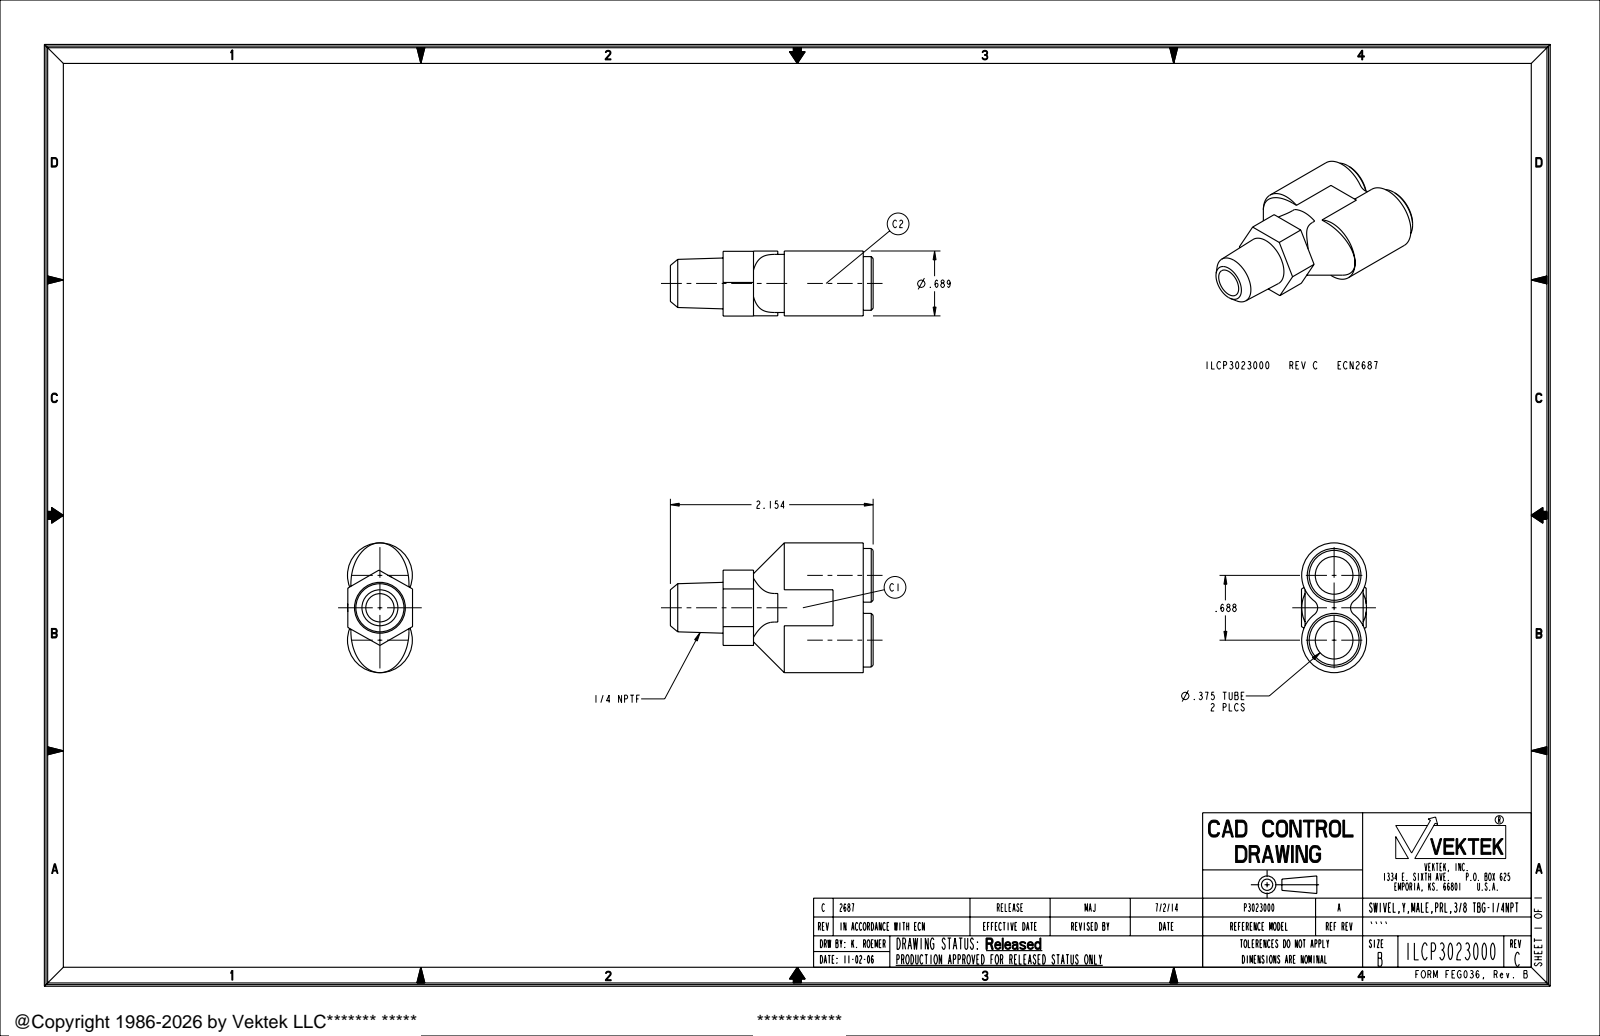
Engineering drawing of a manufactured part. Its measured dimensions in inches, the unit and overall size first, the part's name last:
Units: inches
Overall size (bounding box): 2.154 × 1.378 × 0.691
Round holes (diameter × count): ⌀0.4 ×2, ⌀0.3 ×1
Round bosses / shafts (diameter × count): ⌀0.57 ×2
Partial cylindrical surfaces — rounded edges, fillets, slot ends (radius × count): R0.09 ×2, R0.309 ×2, R0.344 ×2, R0.344 ×1
Main face-to-face distances: 0.495, 0.617, 0.105, 0.6, 1.594, 1.489, 0.994, 0.033, 0.65, 0.687
Hole centre spacings: 0.344, 0.688
Volume: 0.926 in³ · Surface area: 9.811 in²
Bodies: 1 solid, 55 faces (29 planar, 18 cylindrical, 8 other)
Part name (STEP PRODUCT): ILCP3023000
STEP written by: PRO/ENGINEER BY PARAMETRIC TECHNOLOGY CORPORATION, 2013320 (CONFIG_CONTROL_DESIGN)
